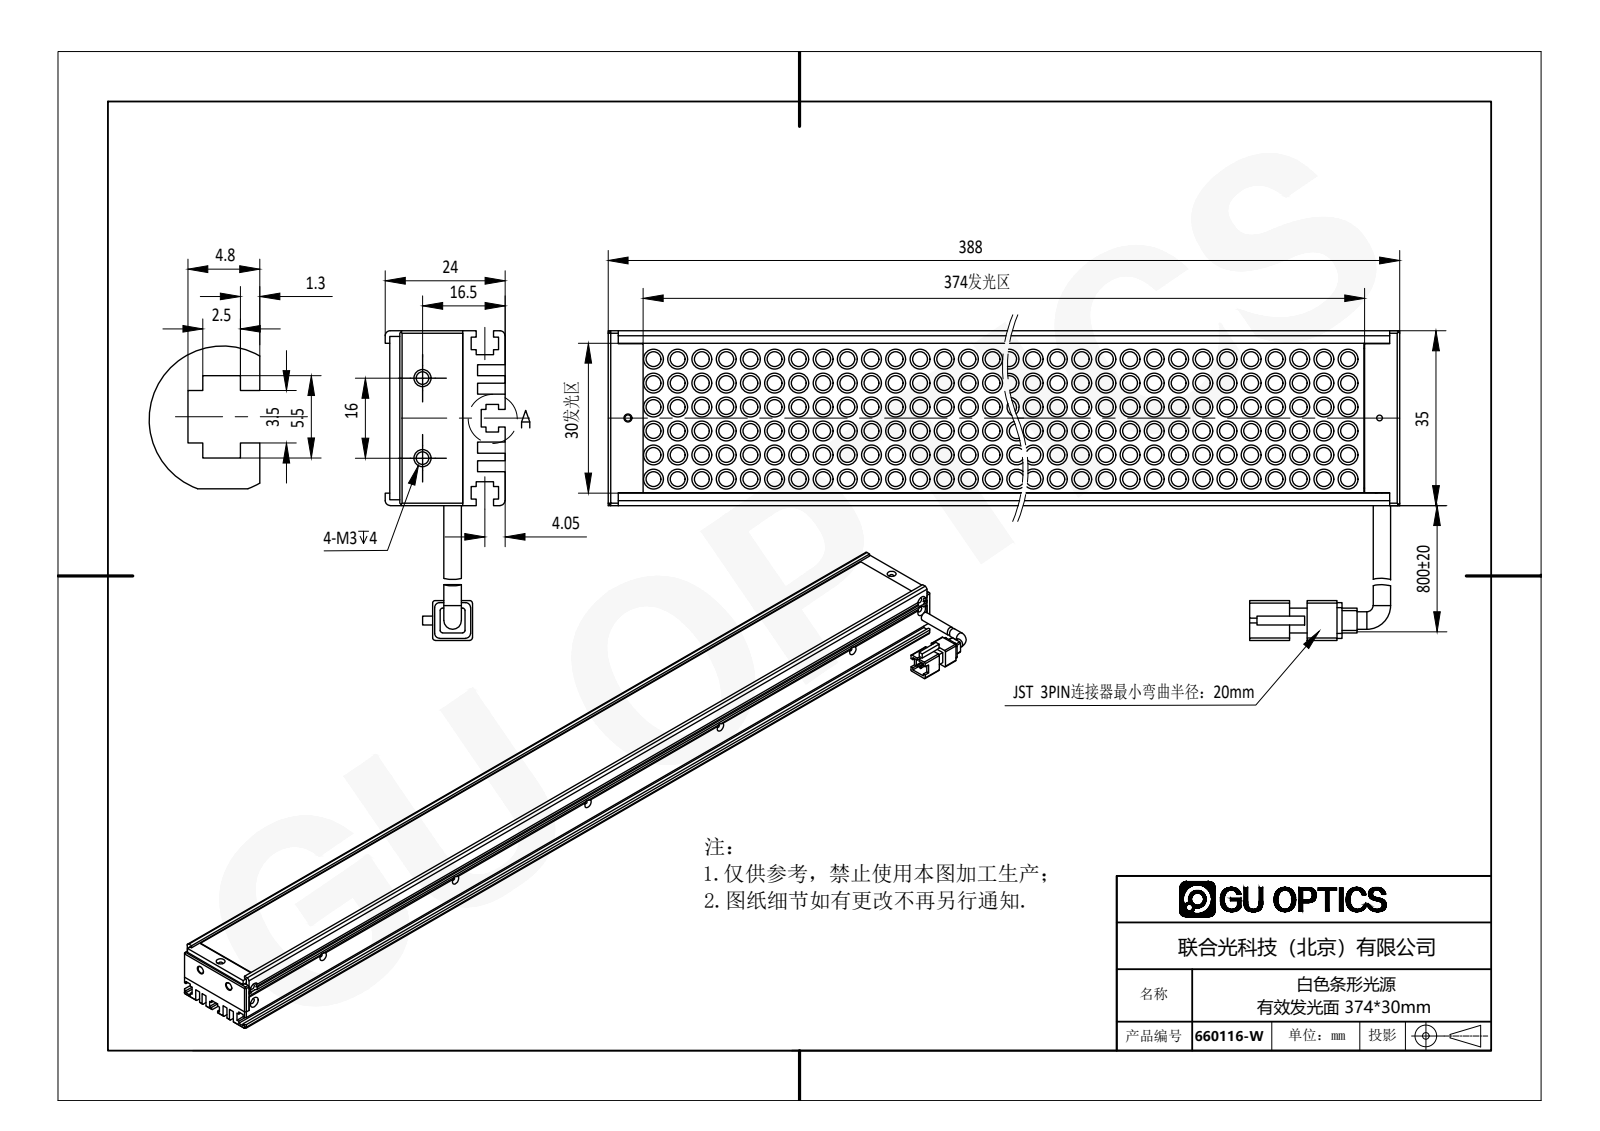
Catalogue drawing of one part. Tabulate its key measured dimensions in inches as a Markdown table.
| quantity | value |
| --- | --- |
| part name | 660116-W |
| STEP written by | SolidWorks 2016 (AUTOMOTIVE_DESIGN) |
| units | inches |
| bodies | 9 solids, 3090 faces (746 planar, 1783 cylindrical, 561 other) |
| overall size | 15.276 × 2.441 × 0.945 |
| volume | 10.13 in³ |
| surface area | 297.7 in² |
| round holes (diameter × count) | 0.049 × 7, 0.063 × 5, 0.087 × 5, 0.067 × 2, 0.098 × 2, 0.118 × 2 |
| round bosses / shafts (diameter × count) | 0.157 × 420, 0.118 × 420, 0.138 × 2 |
| partial cylindrical surfaces (radius × count) | 0.039 × 12, 0.02 × 8, 0.065 × 1 |
| main face-to-face distances | 0.079, 0.087, 0.472, 0.126, 0.039, 0.335, 0.346, 0.551, 0.433, 0.098 |
| hole center spacings | 2.953, 14.961, 5.906, 0.022, 0.276, 7.442, 8.858, 13.347 |
